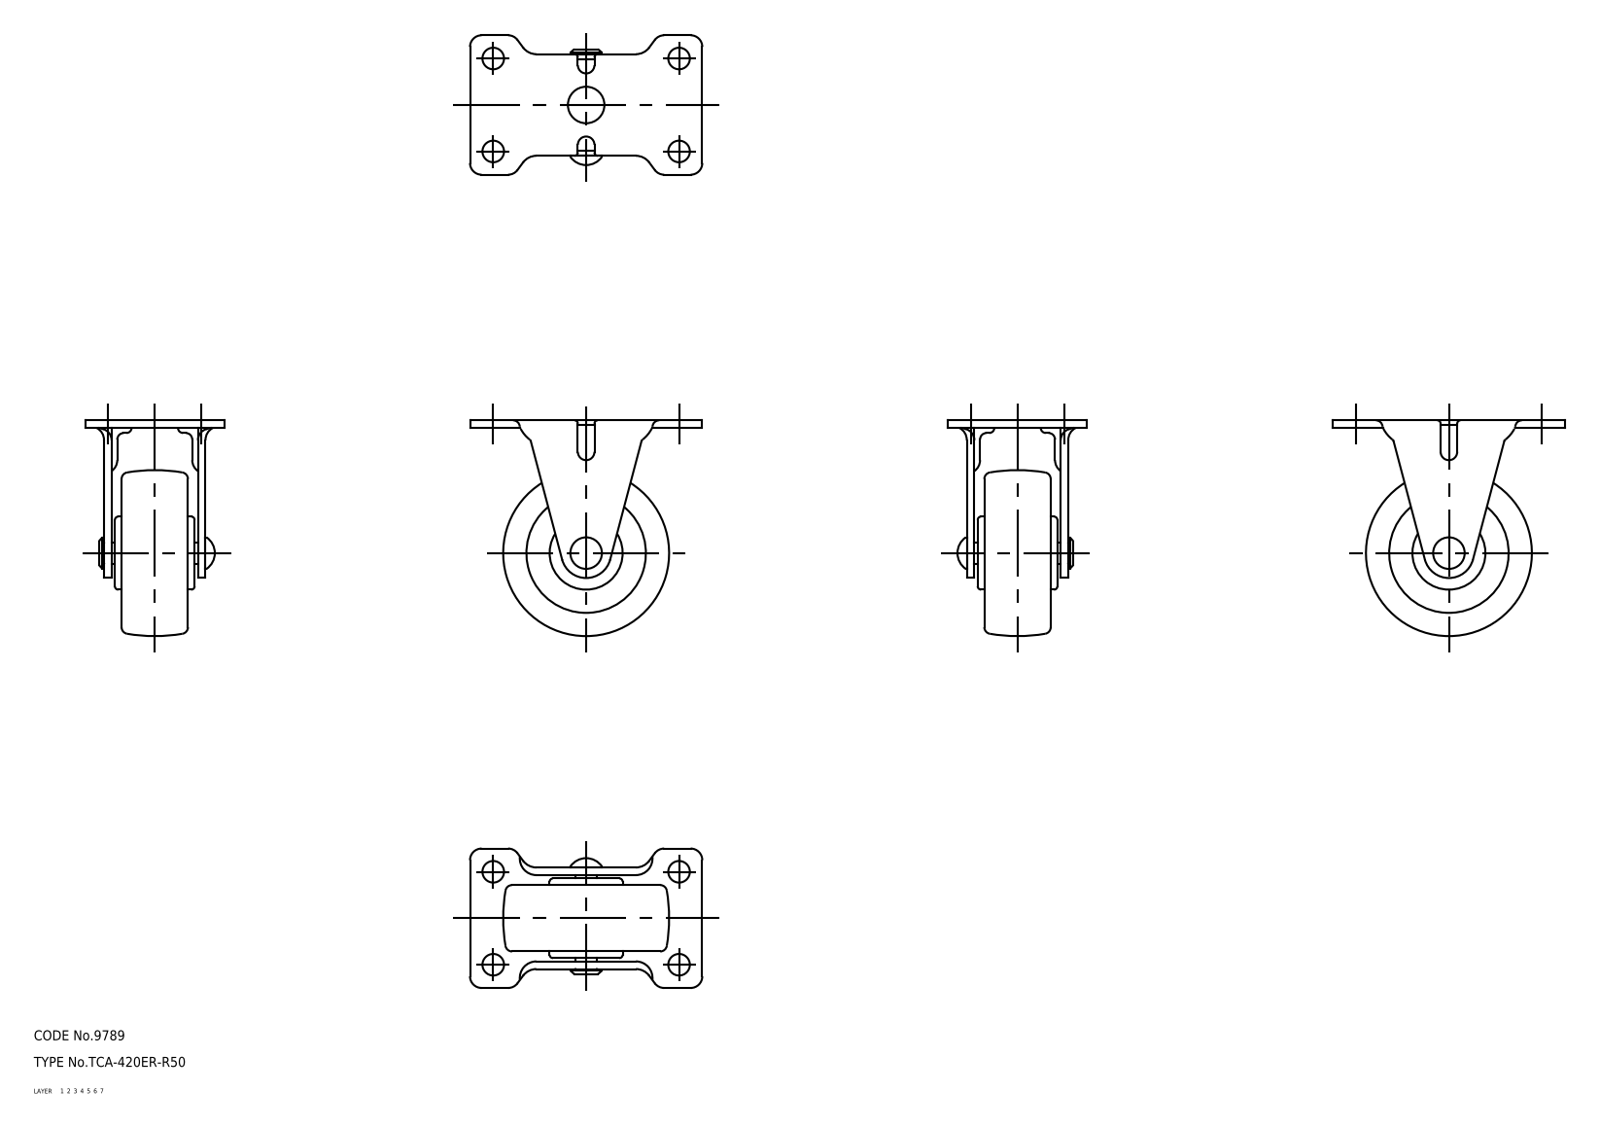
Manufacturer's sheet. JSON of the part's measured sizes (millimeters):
{"part_name": "wheel; axle; No_420_ER_R50_1_30693_36", "step_written_by": "CADfix (AUTOMOTIVE_DESIGN)", "units": "millimeters", "bodies": {"solids": 3, "faces": 166, "planar": 0, "cylindrical": 0, "other": 166}, "overall_size": [70, 65, 42], "volume_mm3": 49135, "surface_area_mm2": 18067}
